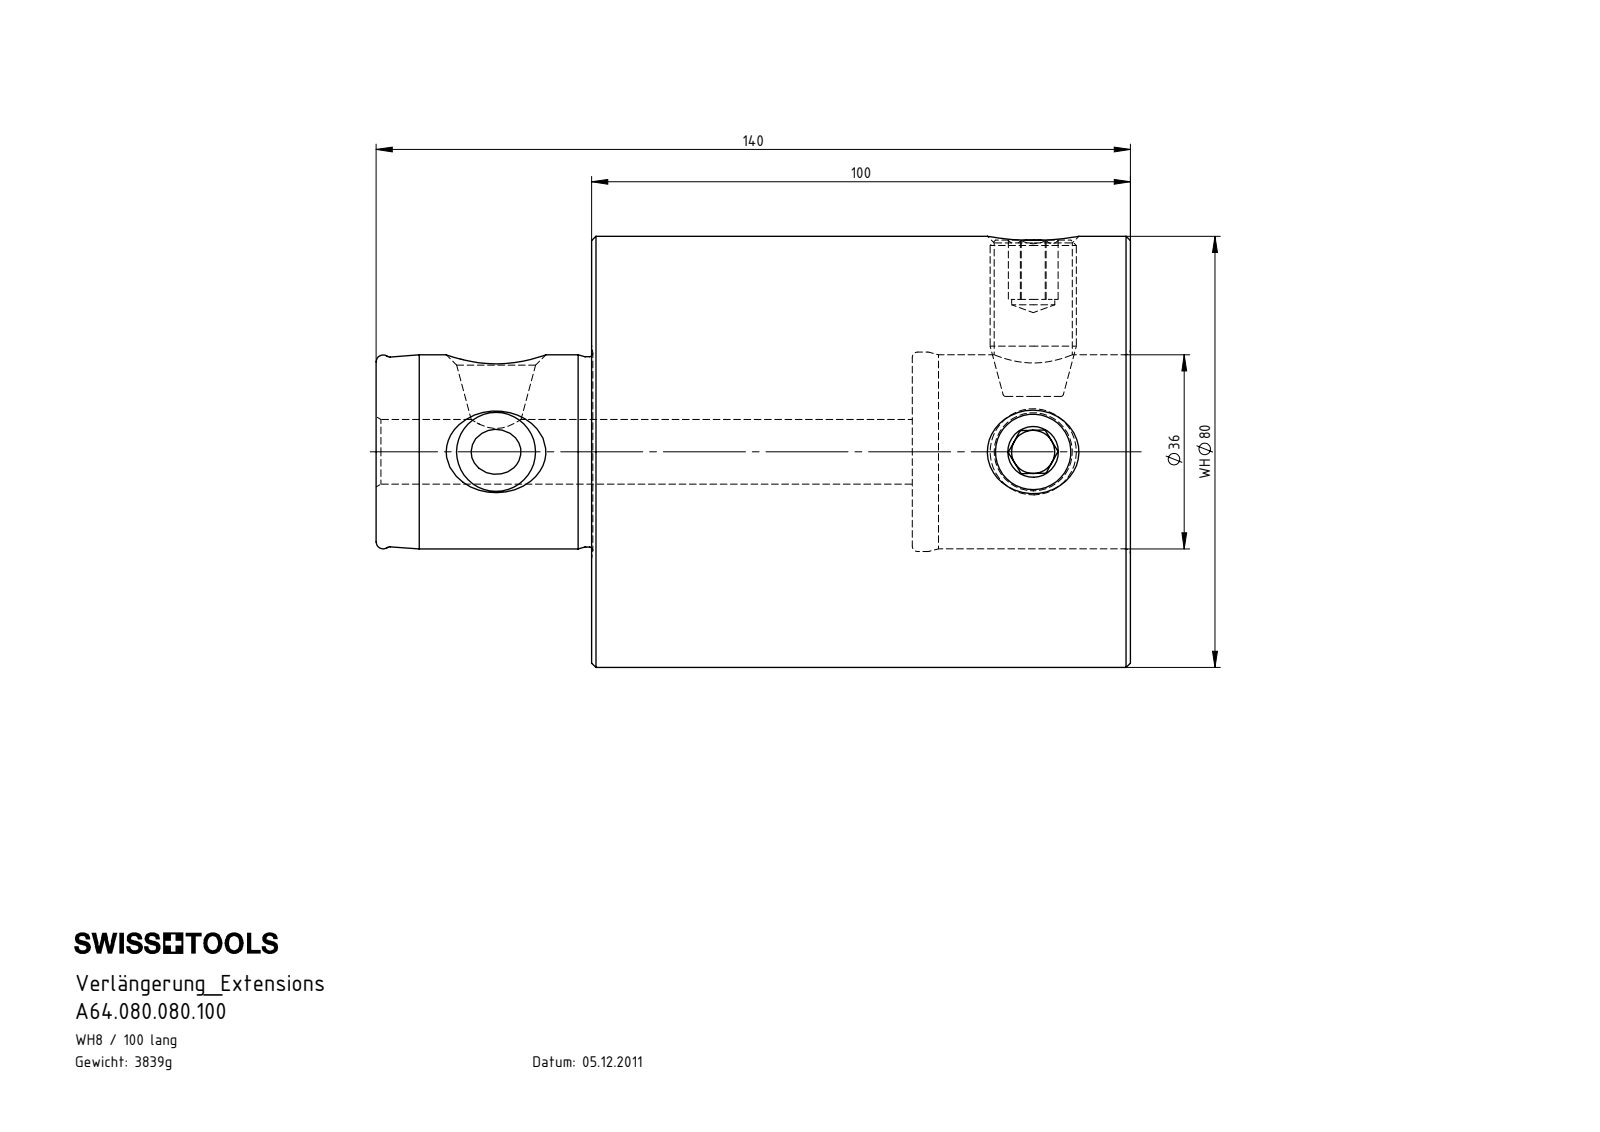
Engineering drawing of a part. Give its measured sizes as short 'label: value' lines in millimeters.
name: WH8.WH8.001.100; WH8-ER1.001.029; WH8-WH8.001.100_B
written by: SolidWorks 2017 (AUTOMOTIVE_DESIGN)
unit: mm
bodies: 3 solids, 75 faces (32 planar, 12 cylindrical, 31 other)
size: 140 × 80 × 80
volume: 489 072 mm³; area: 53 207 mm²
holes: 2× ⌀8, 2× ⌀14.5, 1× ⌀12, 1× ⌀36, 1× ⌀37
bosses: 2× ⌀16, 1× ⌀80, 1× ⌀35.3
face distances: 100, 59.5, 40.5, 40, 99.5, 140, 8, 29, 18, 11
